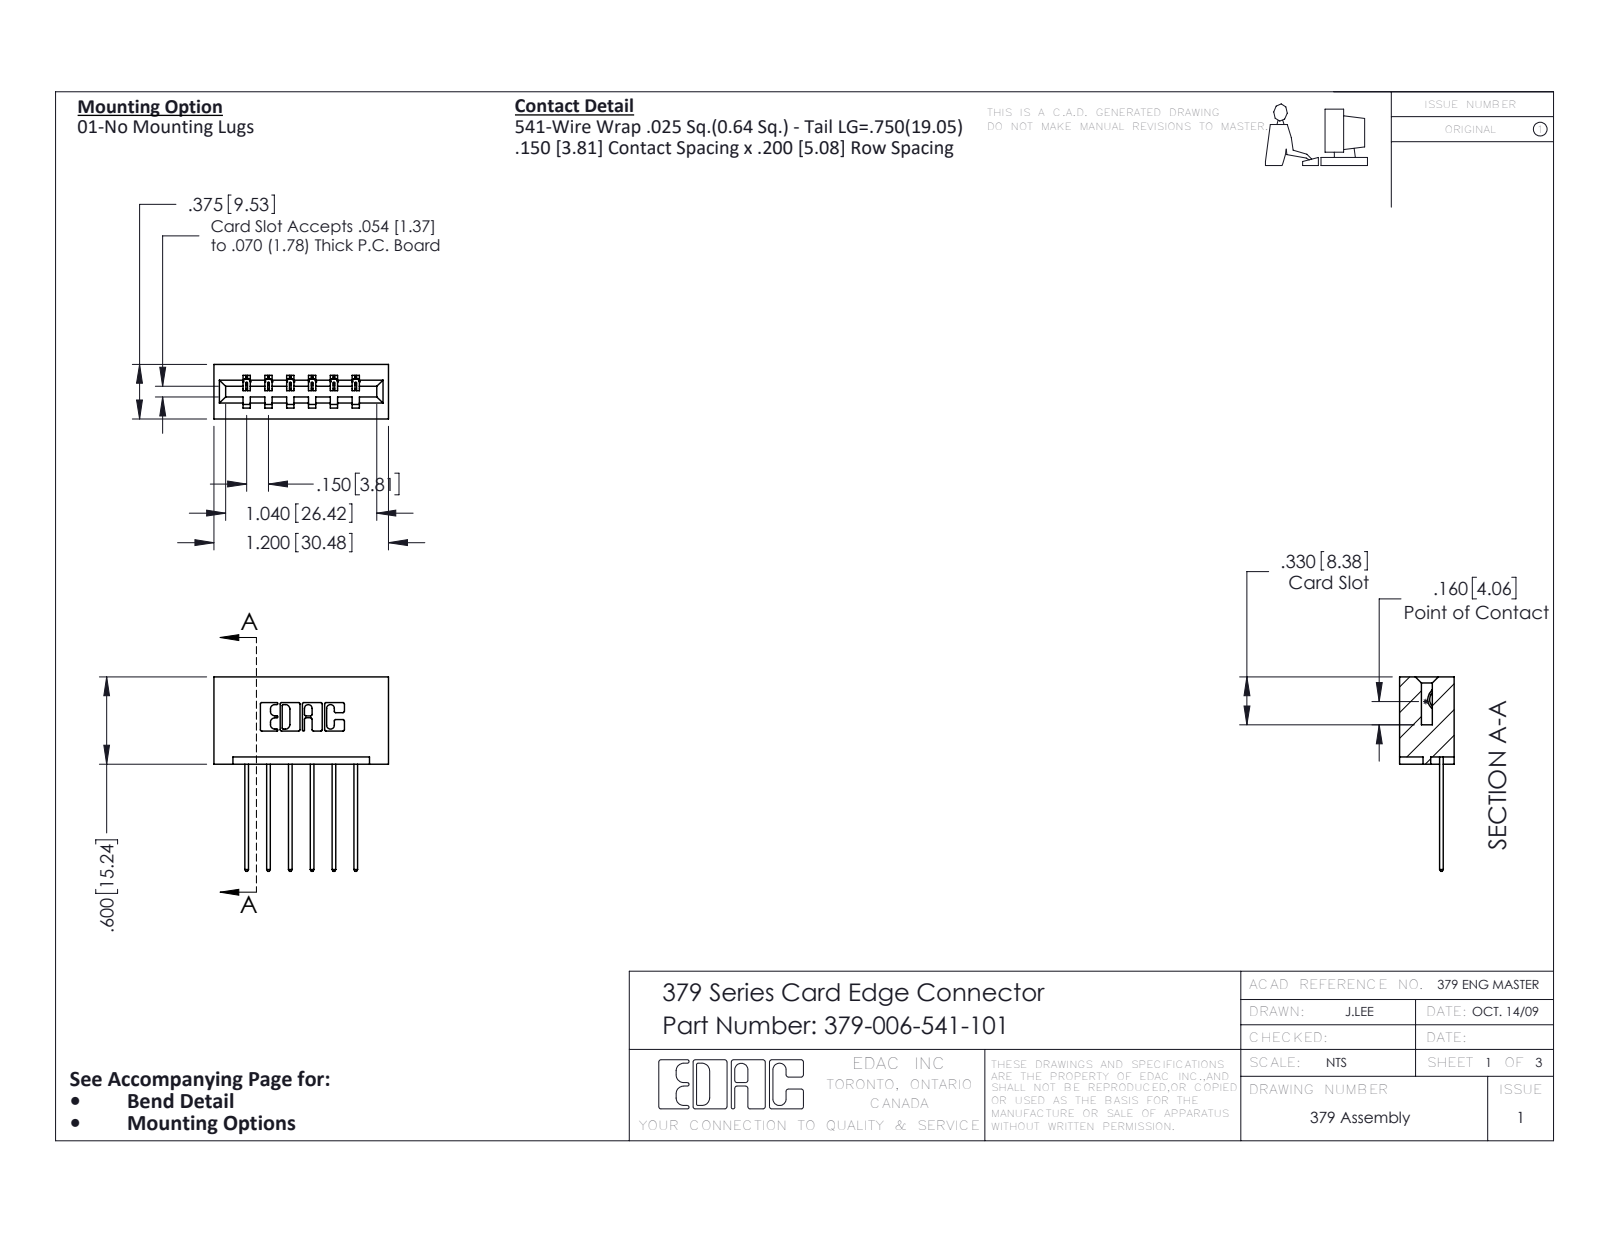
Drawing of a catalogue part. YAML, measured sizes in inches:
part_name: "379 Part_Lugless; 379-006-541-101; 345-292-001_345-293-141"
step_written_by: "SolidWorks 2016 (CONFIG_CONTROL_DESIGN)"
units: inches
bodies: {solids: 7, faces: 454, planar: 318, cylindrical: 136, other: 0}
overall_size: [1.337, 1.2, 0.375]
volume: 0.214
surface_area: 5.429
partial_cylinders:
  - {radius: 0.01, count: 22}
  - {radius: 0.006, count: 12}
  - {radius: 0.01, count: 12}
  - {radius: 0.007, count: 6}
  - {radius: 0.031, count: 6}
  - {radius: 0.026, count: 3}
  - {radius: 0.014, count: 1}
  - {radius: 0.022, count: 1}
face_to_face_distances: [0.3, 0.15, 0.2, 0.075, 0.1, 0.375, 0.05, 0.55, 0.45, 0.6]
